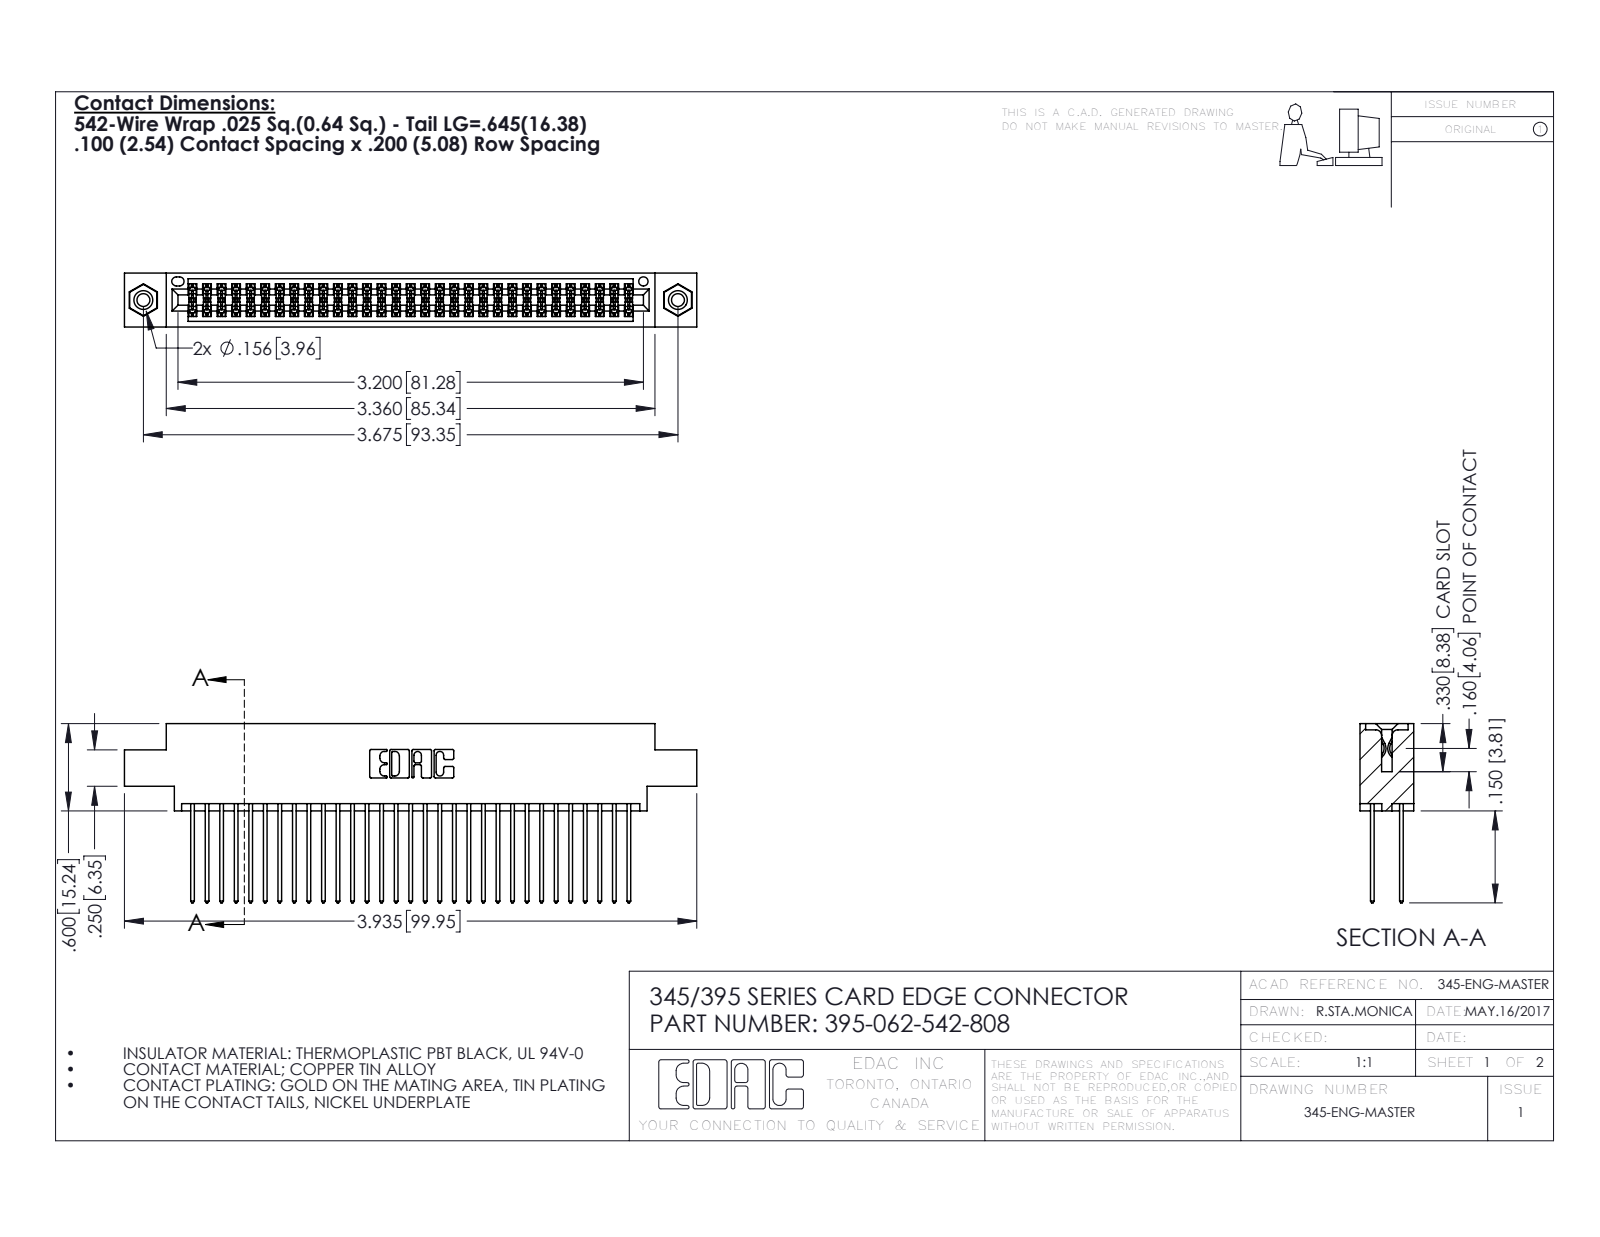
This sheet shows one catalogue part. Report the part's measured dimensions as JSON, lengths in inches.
{"part_name": "345-250-001_345-250-003-102; 395-062-542-808; 345 Part_0.170 Offset - 0.156 Dia-TI; 345-292-001_345-293-142", "step_written_by": "SolidWorks 2016 (CONFIG_CONTROL_DESIGN)", "units": "inches", "bodies": {"solids": 65, "faces": 3290, "planar": 2162, "cylindrical": 1112, "other": 16}, "overall_size": [3.935, 1.232, 0.37], "volume_in3": 0.597, "surface_area_in2": 24.41, "round_holes": [[0.089, 2], [0.125, 2], [0.156, 2], [0.064, 1]], "round_bosses_or_shafts": [[0.155, 2]], "partial_cylinders_radius": [[0.006, 93], [0.01, 62], [0.01, 22], [0.007, 6], [0.031, 6], [0.026, 3], [0.014, 2], [0.019, 2]], "face_to_face_distances": [0.072, 0.298, 0.2, 0.098, 0.272, 0.025, 0.37, 0.225, 0.175, 0.149], "hole_center_spacings": [0.27, 3.44, 3.675]}
